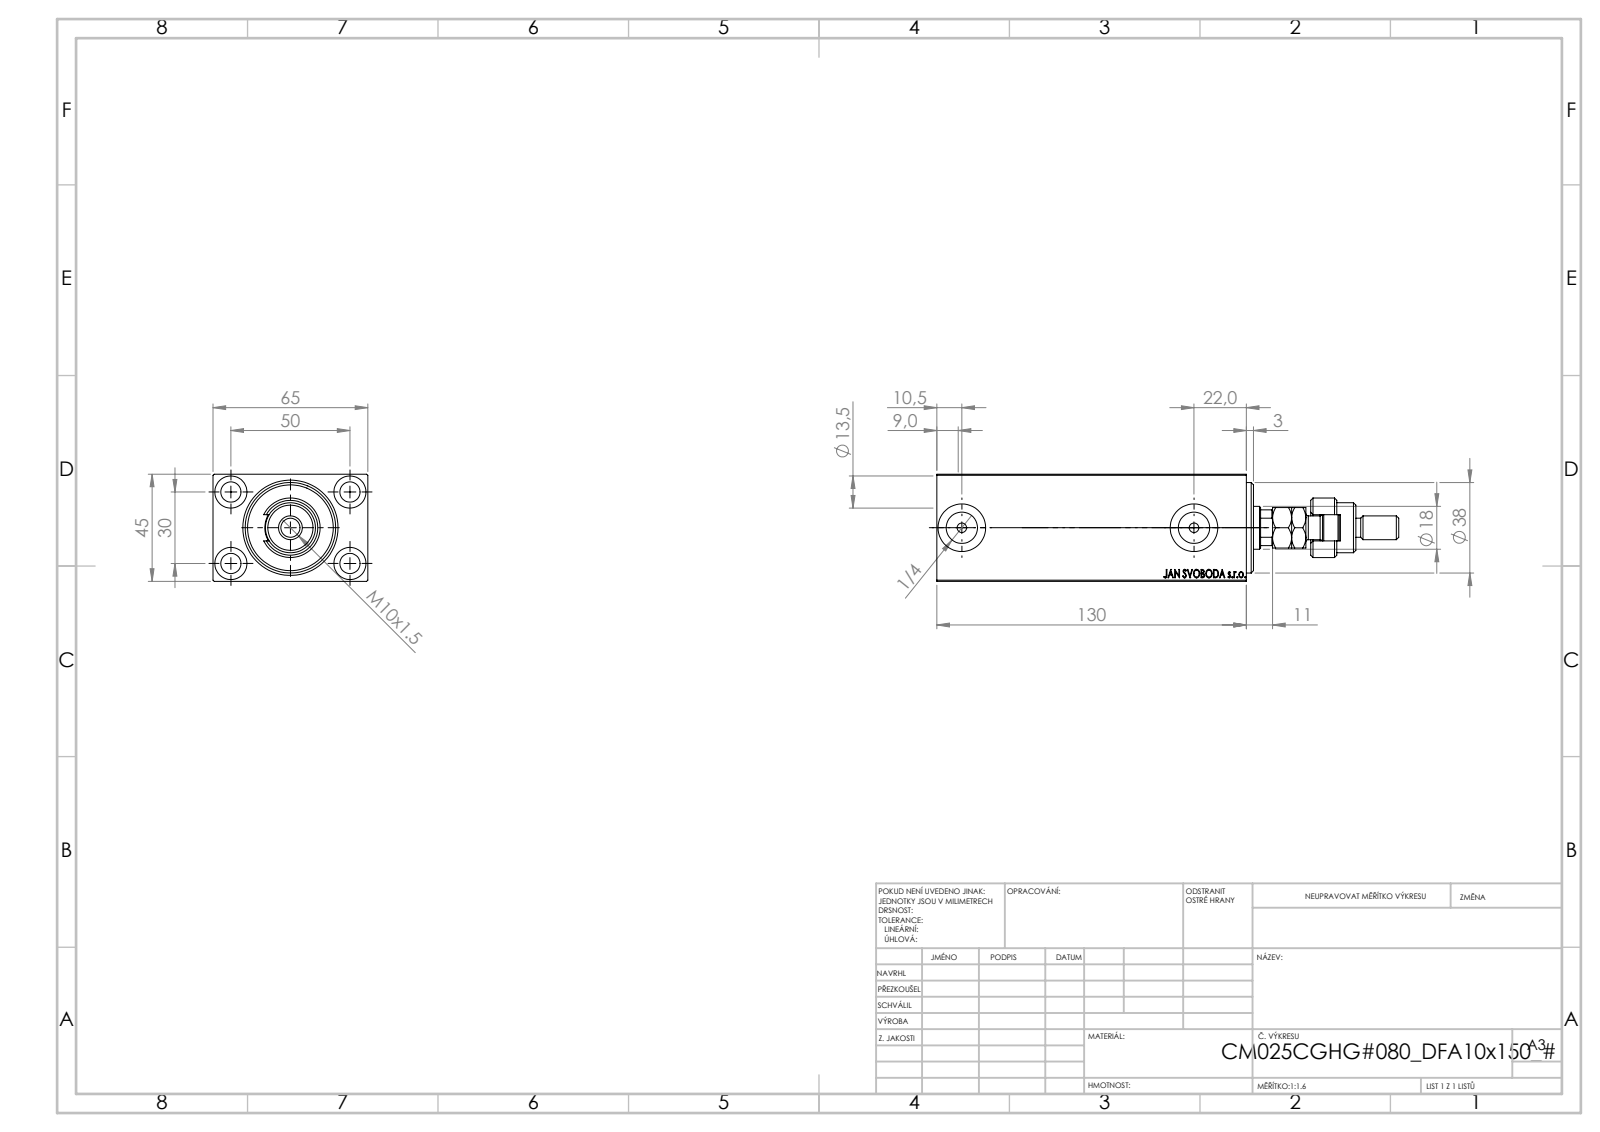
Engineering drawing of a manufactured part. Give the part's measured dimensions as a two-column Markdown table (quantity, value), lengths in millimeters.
| quantity | value |
| --- | --- |
| part name | V450CM_VC_B; V450CM_C_VCP; V450CM_C_Body; FEMALE_PART_FOR_DFA (+1 more) |
| STEP written by | SolidWorks 2019 (CONFIG_CONTROL_DESIGN) |
| units | millimeters |
| bodies | 5 solids, 947 faces (436 planar, 73 cylindrical, 438 other) |
| overall size | 194 × 65 × 45 |
| volume | 337 582 mm³ |
| surface area | 80 810 mm² |
| round holes (diameter × count) | 8.5 × 5, 13.5 × 4, 4 × 2, 13.16 × 2, 20 × 2, 18 × 1, 21.5 × 1, 27 × 1, 38 × 1 |
| round bosses / shafts (diameter × count) | 25 × 1, 21 × 1, 16 × 1, 10 × 1, 8 × 1 |
| partial cylindrical surfaces (radius × count) | 5.5 × 1, 8.5 × 1, 8.75 × 1 |
| main face-to-face distances | 45, 65, 124, 5, 3, 125, 130, 8, 6, 119 |
| hole center spacings | 29.15, 30, 50, 58.31, 97.5 |
